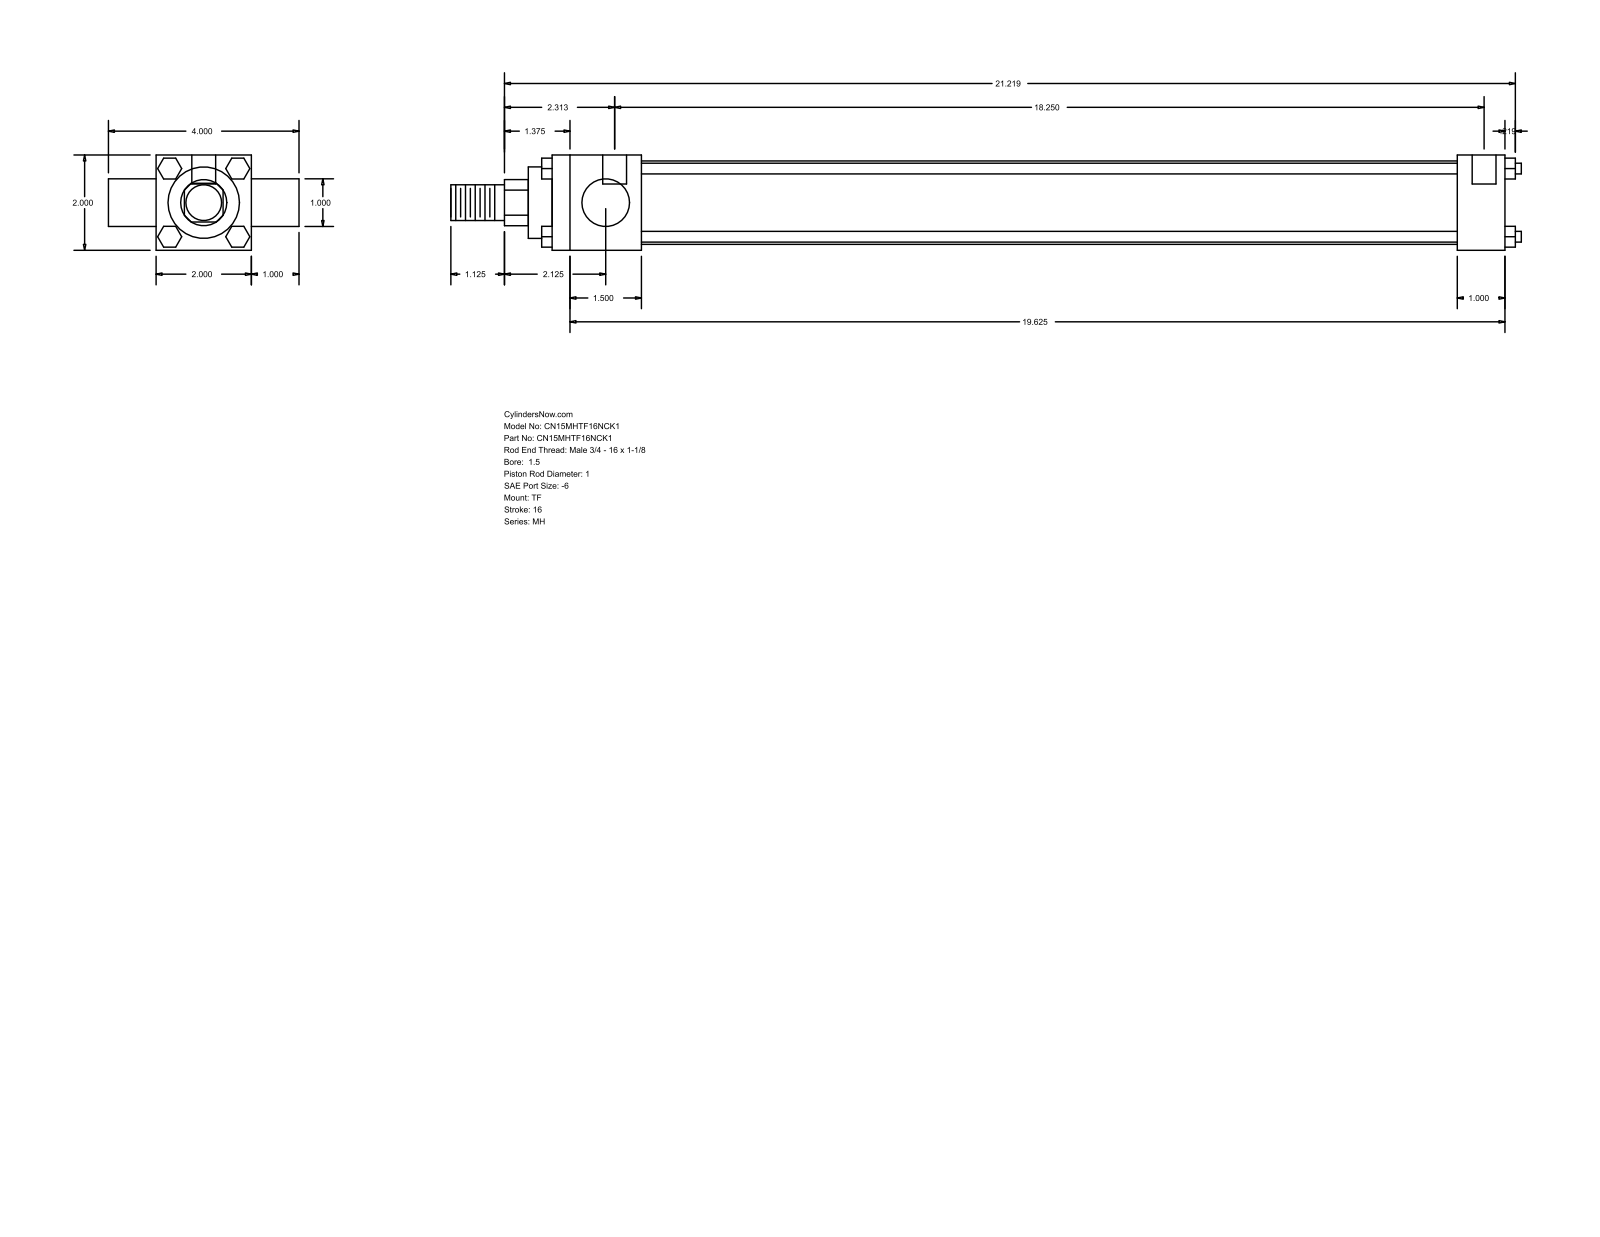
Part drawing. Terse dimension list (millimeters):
name: MH_TF__0150_1
written by: GSSL Pune (CONFIG_CONTROL_DESIGN)
unit: mm
bodies: 0 solids, 120 faces (92 planar, 28 cylindrical, 0 other)
size: 570.71 × 101.6 × 50.8
holes: 3× ⌀5.56, 2× ⌀12.7
bosses: 4× ⌀5.71, 2× ⌀25.4, 1× ⌀44.45, 1× ⌀38.1, 1× ⌀19.05
rounds: 1× R12.29
face distances: 50.8, 25.4, 508, 76.2, 47.63, 460.37, 482.6, 434.97, 101.6, 12.7
hole spacings: 3.18, 463.55, 466.73
